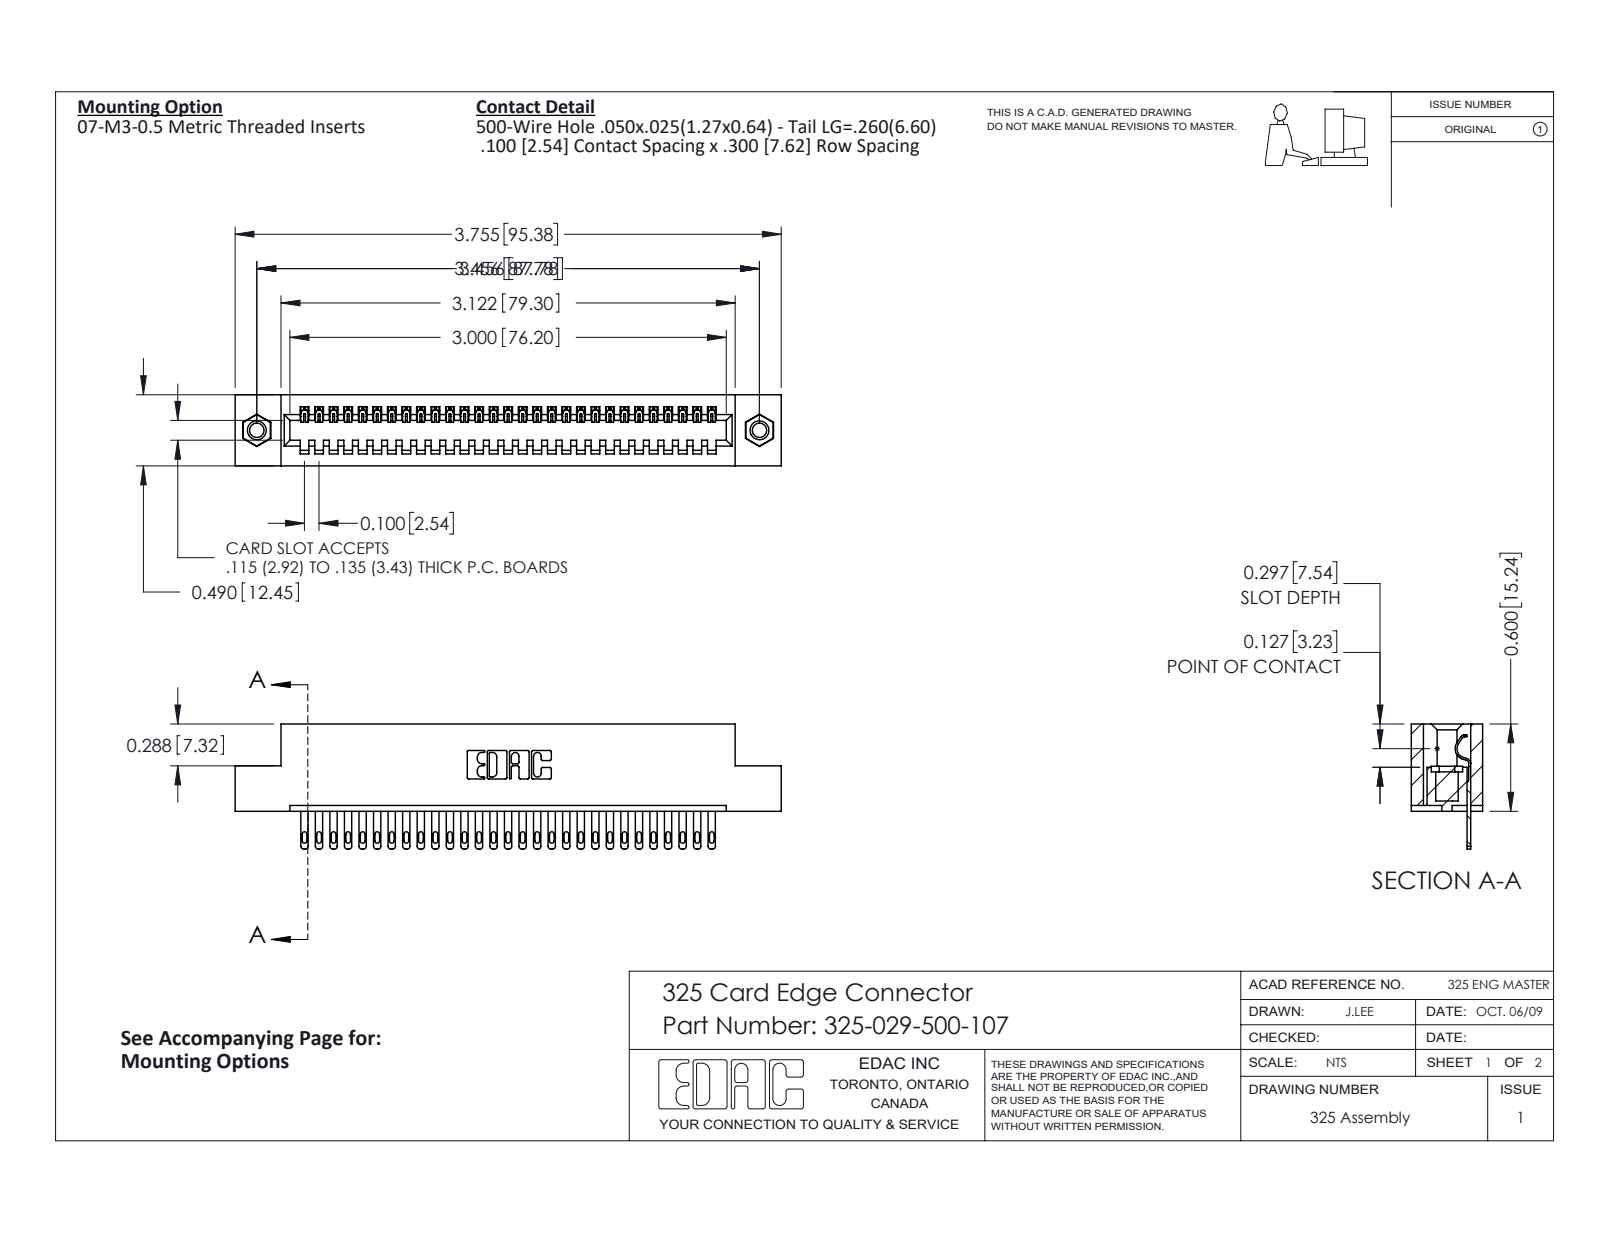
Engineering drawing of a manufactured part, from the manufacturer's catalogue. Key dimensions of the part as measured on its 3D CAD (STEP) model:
Part name (STEP PRODUCT): 345-250-001_345-250-005-103; 325-292-001_325-293-100; 325-029-500-107; 325 Part_TI
STEP written by: SolidWorks 2016 (CONFIG_CONTROL_DESIGN)
Units: inches
Bodies: 32 solids, 1740 faces (1146 planar, 578 cylindrical, 16 other)
Overall size (bounding box): 3.755 × 0.86 × 0.49
Volume: 0.733 in³ · Surface area: 20.14 in²
Round holes (diameter × count): ⌀0.098 ×2, ⌀0.125 ×2, ⌀0.16 ×2
Round bosses / shafts (diameter × count): ⌀0.155 ×2
Partial cylindrical surfaces — rounded edges, fillets, slot ends (radius × count): R0.006 ×58, R0.016 ×58, R0.02 ×58, R0.01 ×22, R0.007 ×6, R0.031 ×6, R0.026 ×3, R0.014 ×1
Main face-to-face distances: 0.083, 0.407, 0.49, 0.3, 0.107, 0.383, 0.025, 0.325, 0.04, 0.1
Hole centre spacings: 3.456
